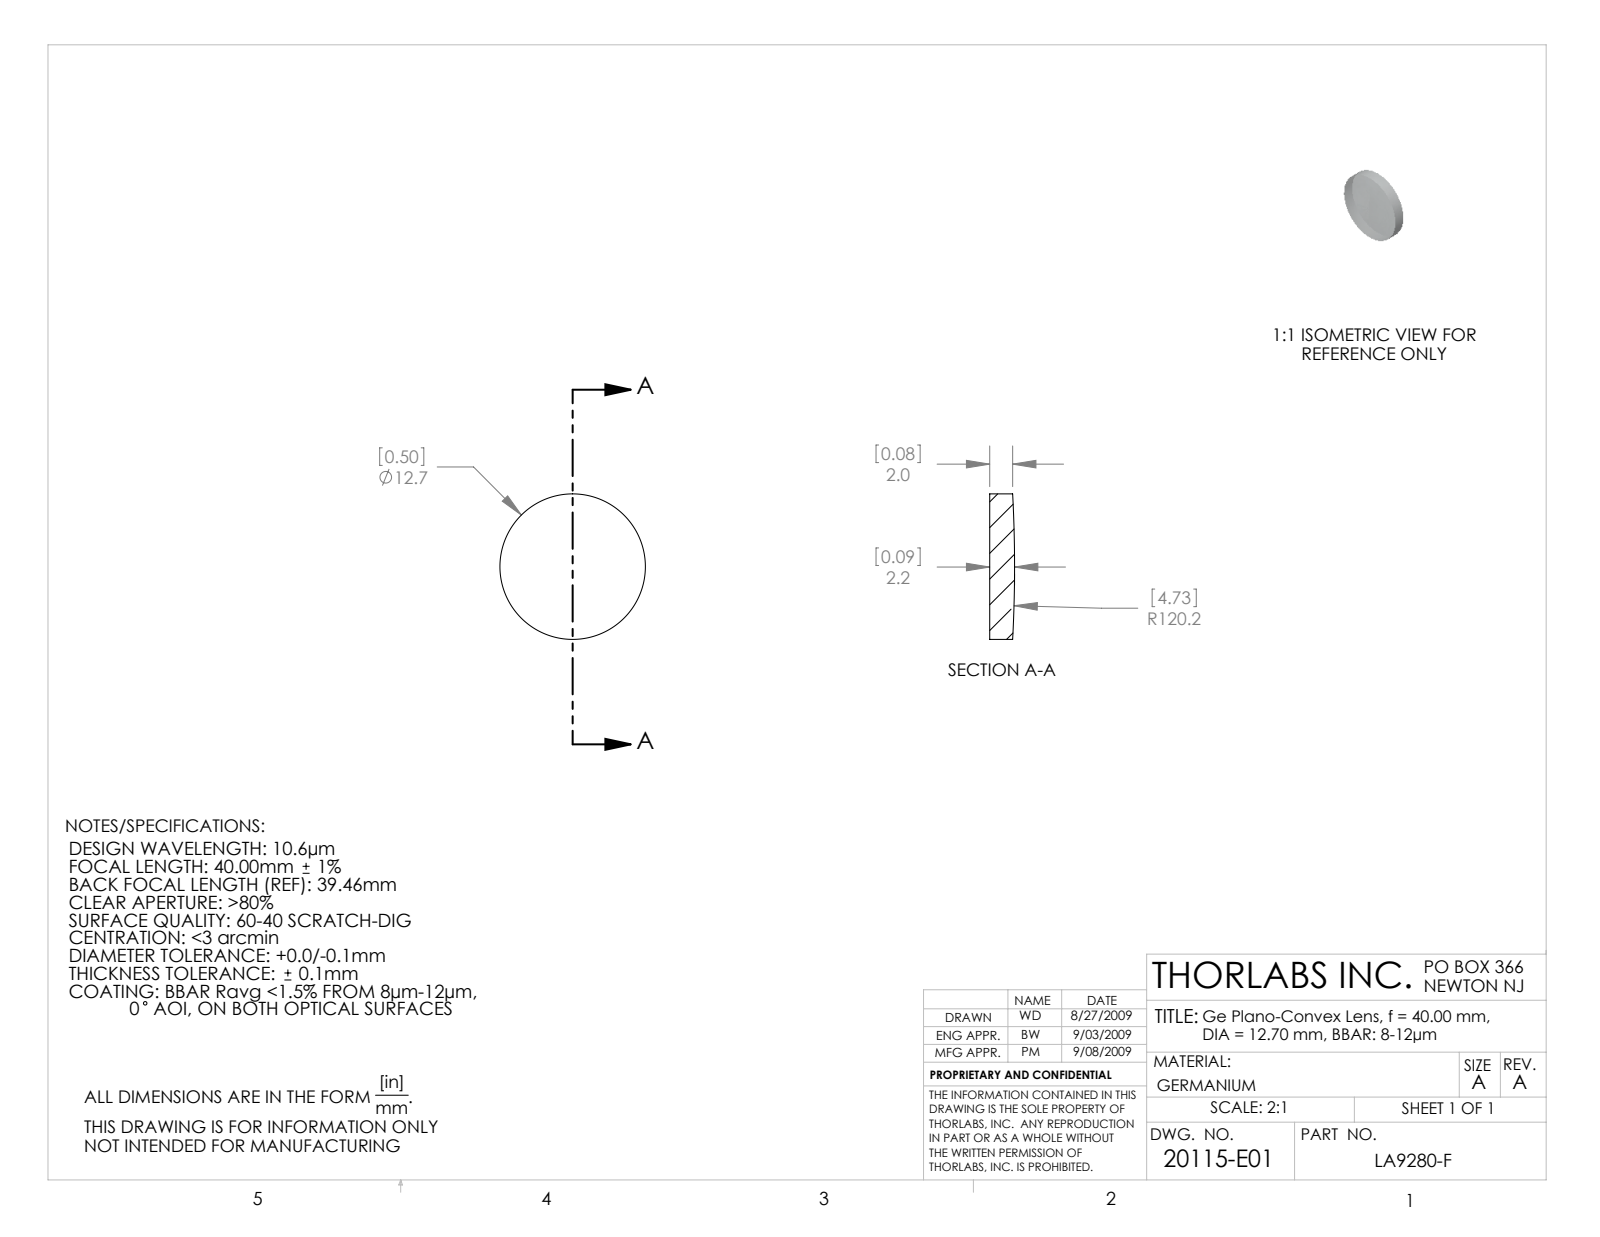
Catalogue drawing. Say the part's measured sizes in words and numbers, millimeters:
The part is named "20115-E0W". Its 3-D file was written by "SolidWorks 2007 (CONFIG_CONTROL_DESIGN)". It is 1 solid with 5 faces: 1 planar, 2 cylindrical and 2 other. Overall it measures 12.7 by 12.7 by 2.17 millimeters. Its volume is 264 cubic millimeters and its surface area 333 square millimeters. Round bosses or shafts: 1 of diameter 12.7.
